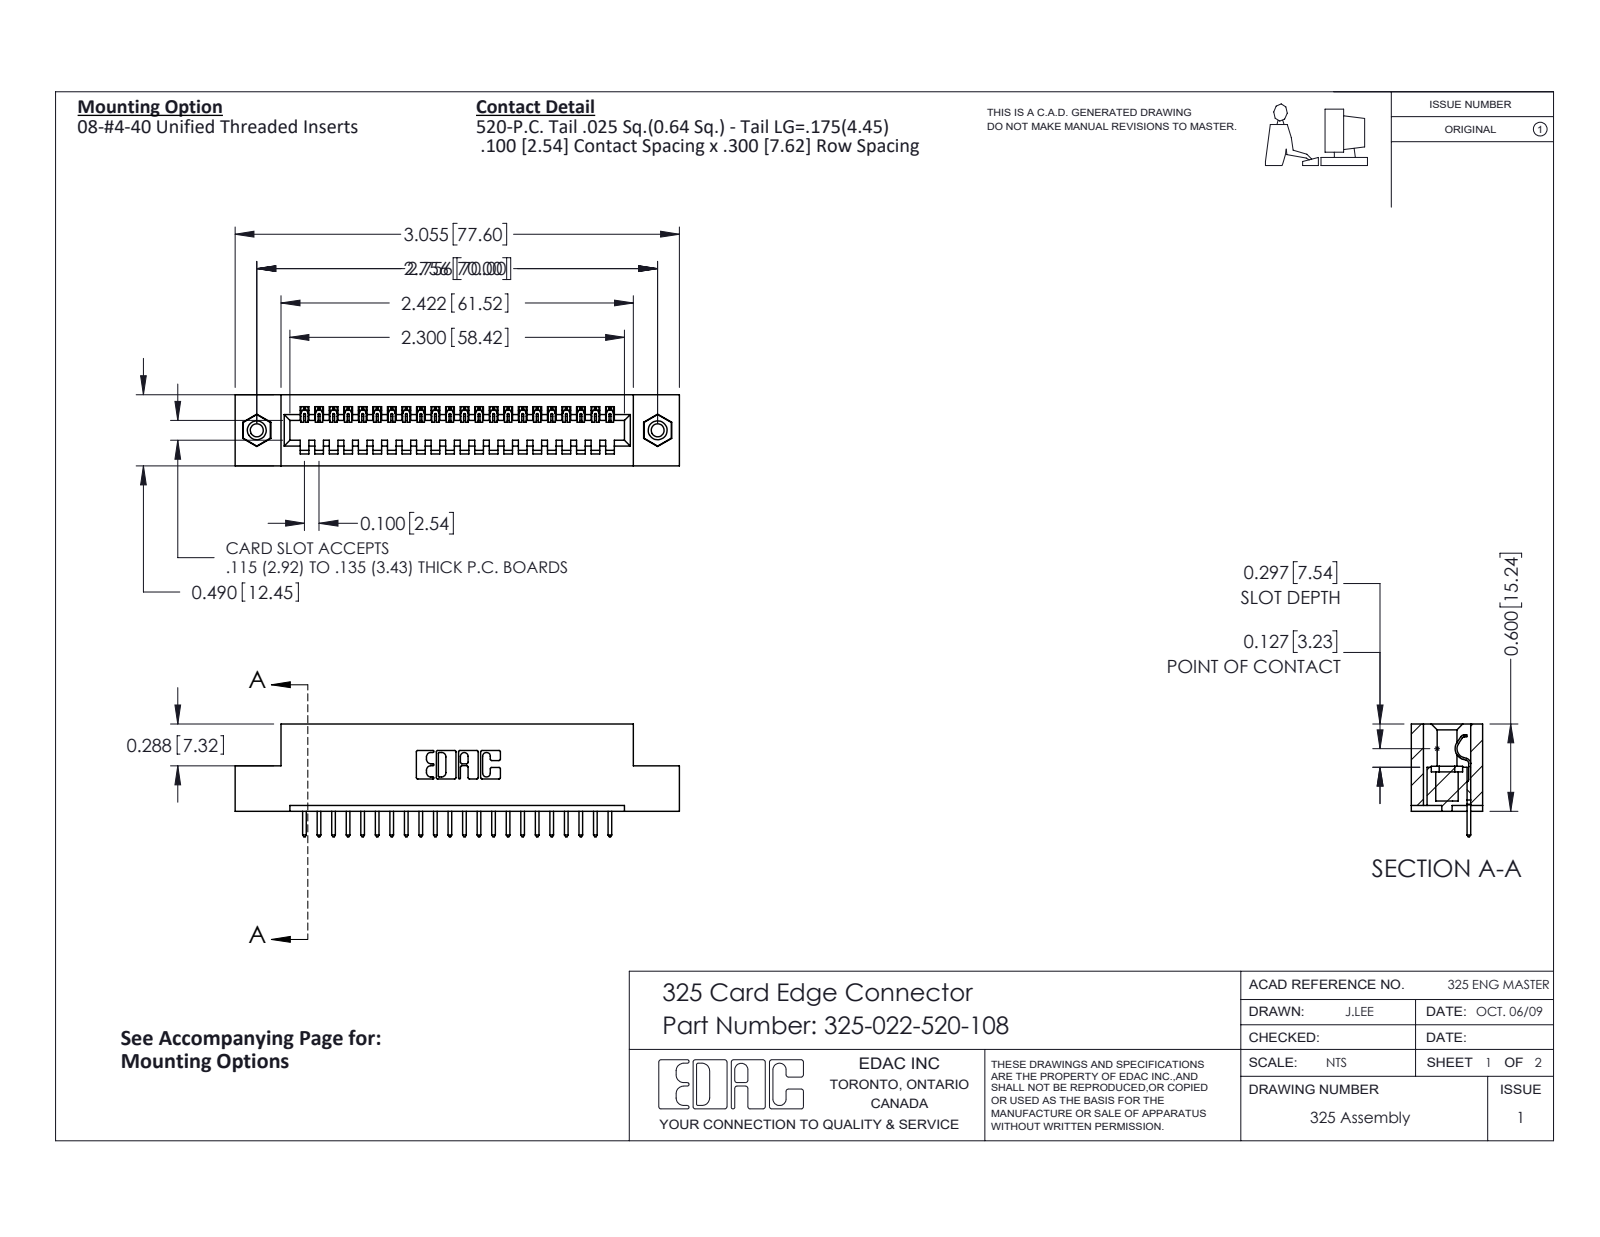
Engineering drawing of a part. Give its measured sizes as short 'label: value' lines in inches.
name: 325 Part_TI; 325-022-520-108; 325-292-001_325-293-120; 345-250-001_345-250-003-102
written by: SolidWorks 2016 (CONFIG_CONTROL_DESIGN)
unit: in
bodies: 25 solids, 1450 faces (1026 planar, 408 cylindrical, 16 other)
size: 3.055 × 0.775 × 0.49
volume: 0.588 in³; area: 15.45 in²
holes: 2× ⌀0.089, 2× ⌀0.125, 2× ⌀0.16
bosses: 2× ⌀0.155
rounds: 44× R0.006, 44× R0.01, 22× R0.01, 6× R0.007, 6× R0.031, 3× R0.026, 1× R0.014, 1× R0.022
face distances: 0.083, 0.407, 0.49, 0.3, 0.107, 0.383, 0.025, 0.04, 0.325, 0.1
hole spacings: 2.756
